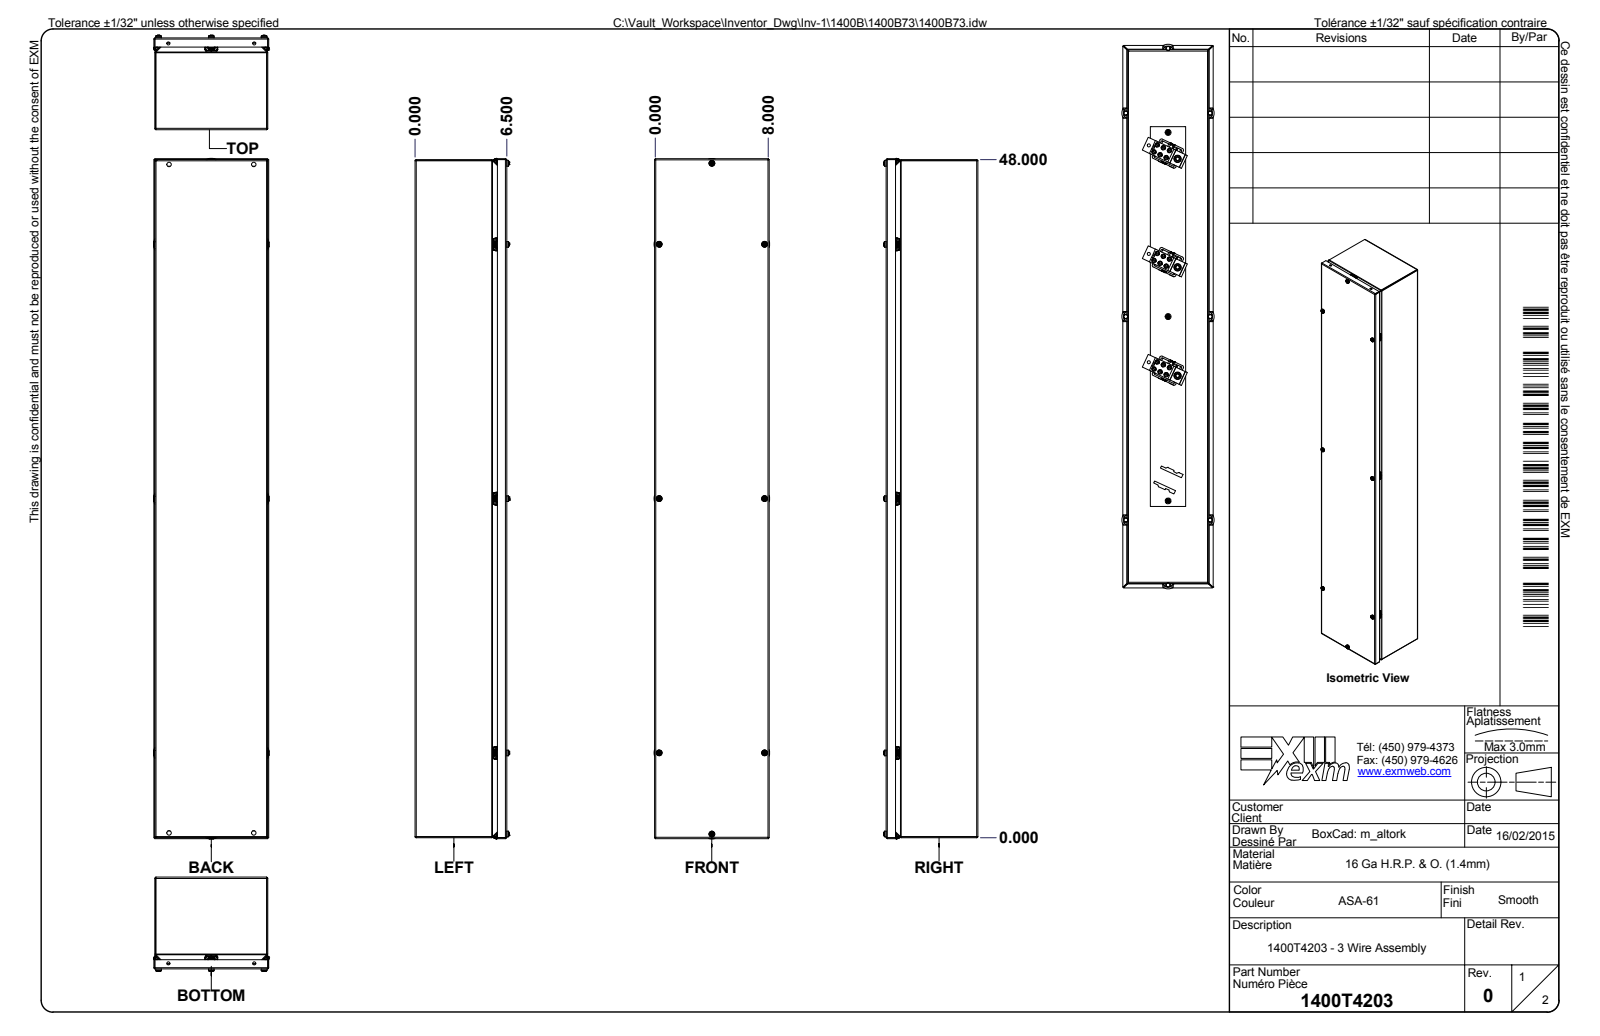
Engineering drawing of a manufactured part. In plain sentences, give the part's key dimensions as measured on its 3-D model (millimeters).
The part is named "1412T4203; 1412T4203B; 1412T4203B-P; RIVET_NUT_M5_FH_OE (+8 more)". Its 3-D file was written by "Autodesk Inventor 2024 (AUTOMOTIVE_DESIGN)". It is 69 solids with 10557 faces: 3640 planar, 3210 cylindrical and 3707 other. Overall it measures 1225.2 by 209.2 by 169.6 millimeters. Its volume is 1 809 000 cubic millimeters and its surface area 2 449 000 square millimeters. Round holes: 18 of diameter 8.5, 8 of diameter 4, 8 of diameter 5, 8 of diameter 7, 6 of diameter 6, 5 of diameter 0.8, 5 of diameter 5.1, 4 of diameter 7.7, 3 of diameter 2, 3 of diameter 5, 3 of diameter 6.7, 3 of diameter 6.8. Round bosses or shafts: 18 of diameter 9.4, 8 of diameter 15, 8 of diameter 7, 8 of diameter 4.9, 8 of diameter 3.5, 3 of diameter 15.7, 3 of diameter 9.5, 3 of diameter 5.9. Partial cylindrical surfaces (rounded edges, fillets, slot ends): 545 of radius 0.5, 352 of radius 0.2, 272 of radius 1, 256 of radius 0.3, 92 of radius 0.1, 57 of radius 2, 40 of radius 1.2, 32 of radius 0.3. The main face-to-face distances are 1.3, 163.8, 201.9, 162.4, 165.1, 200.5, 203.2, 3, 1.4, 204.9. The hole center spacings are 15.1, 23.1, 86.5, 106.1, 137, 176.7, 199.1, 228.
